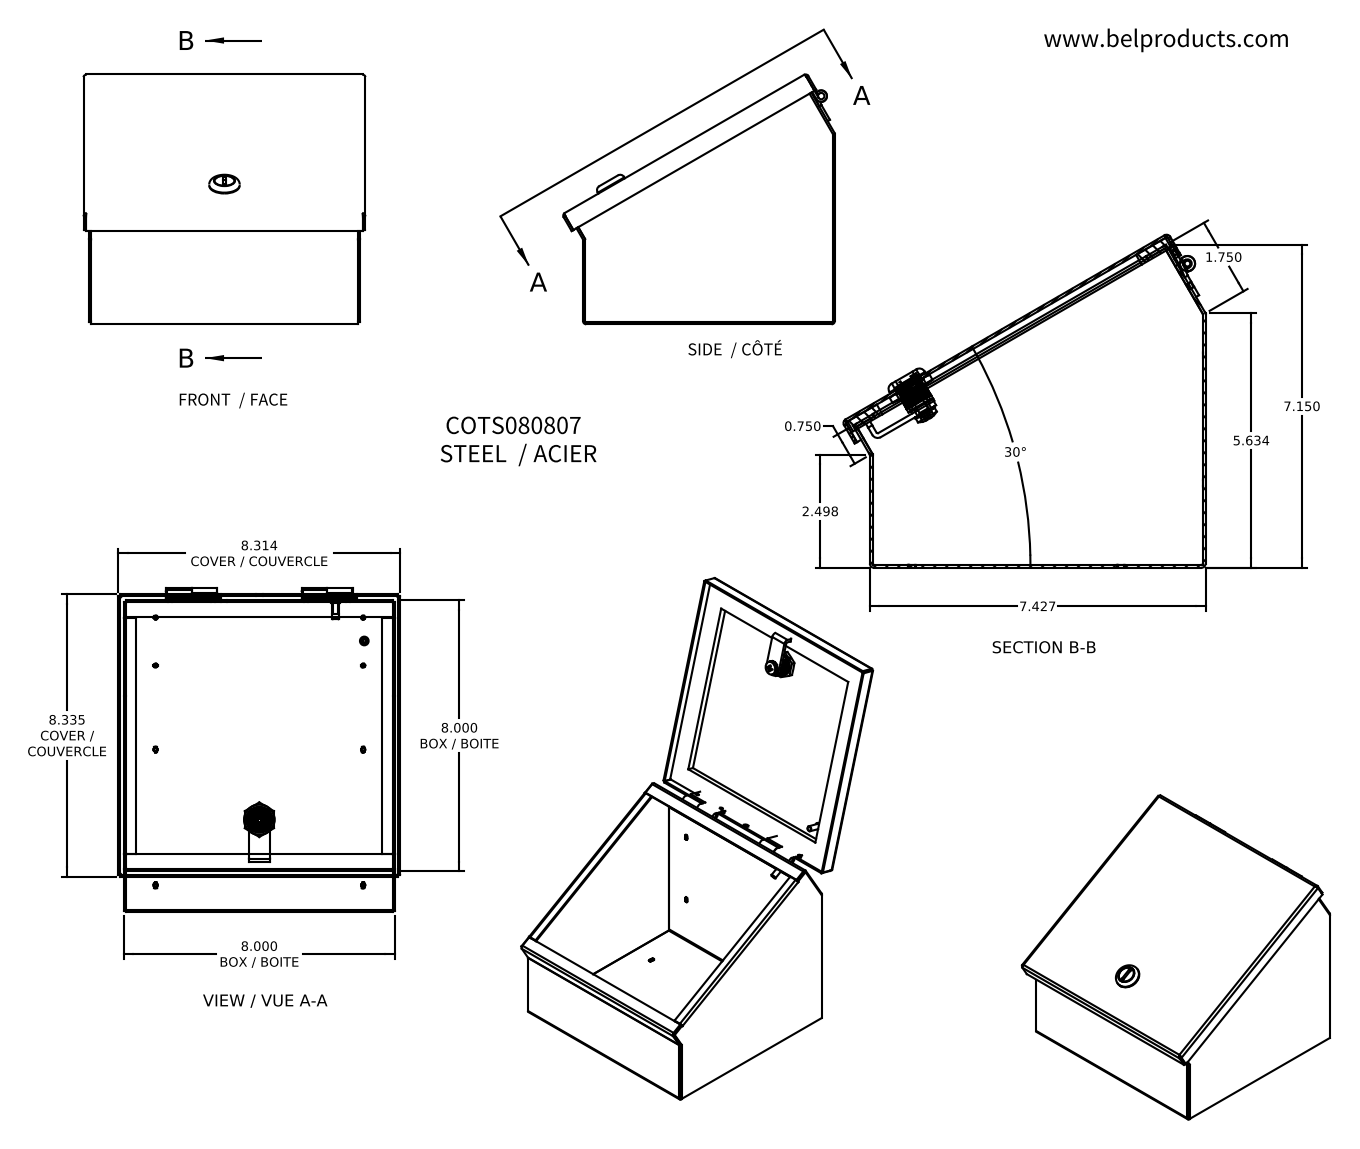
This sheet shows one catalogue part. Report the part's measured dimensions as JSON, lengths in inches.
{"part_name": "LOCK AVEC TOURNEVIS TYPE 4-12 SANS CAME-oa8; HOSING-oa0; INSERT POUR TOURNEVIS-oa1; NOIX DE FIXATION-oa2 (+8 more)", "step_written_by": "Unknown (AUTOMOTIVE_DESIGN)", "units": "inches", "bodies": {"solids": 30, "faces": 1877, "planar": 1200, "cylindrical": 211, "other": 466}, "overall_size": [8.314, 8.012, 7.372], "volume_in3": 30.37, "surface_area_in2": 858.3, "round_holes": [[0.125, 10], [0.13, 8], [0.375, 8], [0.124, 6], [0.169, 1], [0.188, 1], [0.201, 1], [0.275, 1], [0.358, 1], [0.44, 1], [0.505, 1], [0.622, 1]], "round_bosses_or_shafts": [[0.119, 10], [0.25, 8], [0.219, 8], [0.031, 8], [0.125, 6], [0.256, 2], [0.19, 2], [0.02, 2]], "partial_cylinders_radius": [[0.032, 13], [0.092, 12], [0.375, 12], [0.01, 8], [0.371, 2], [0.137, 1], [0.169, 1], [0.169, 1]], "face_to_face_distances": [0.06, 7.94, 0.075, 0.565, 0.506, 0.641, 0.581, 8, 7.88, 7.367], "hole_center_spacings": [1.25, 4, 6.124, 6.125, 0.906, 0.907, 1.544, 1.613]}
